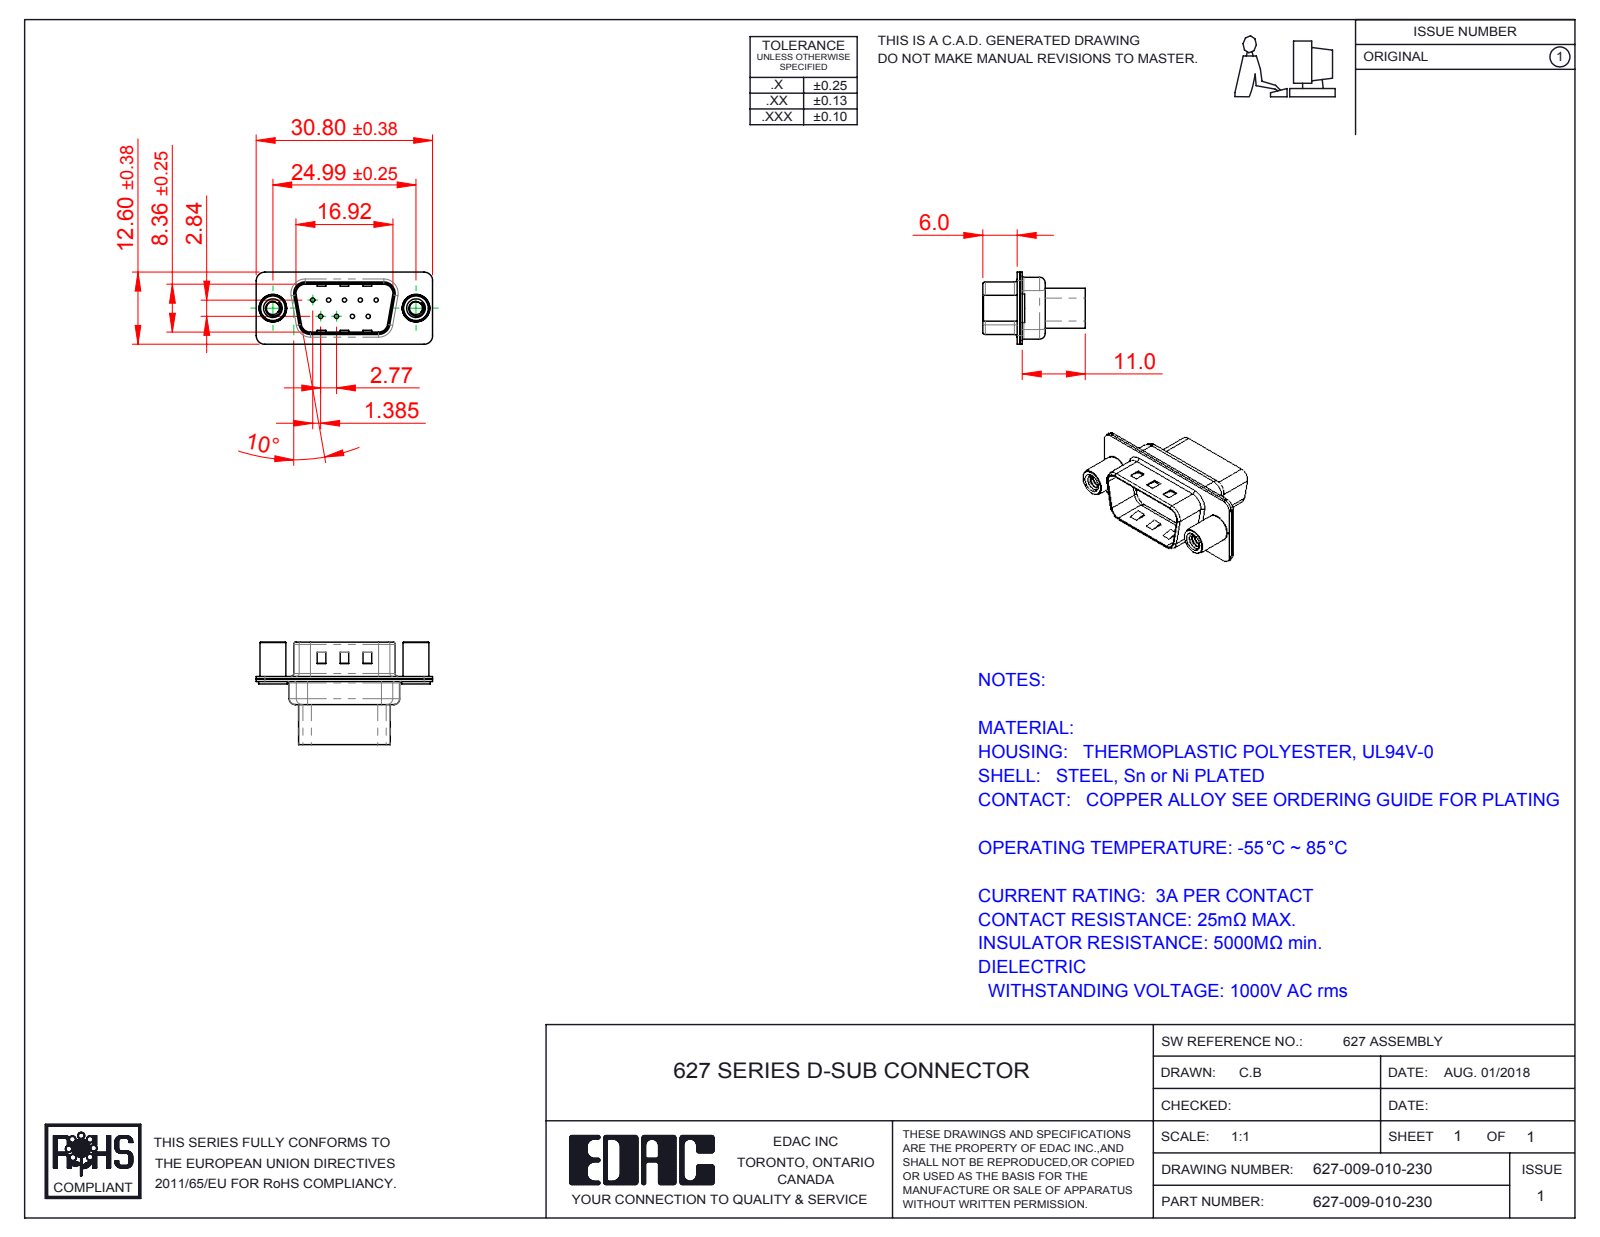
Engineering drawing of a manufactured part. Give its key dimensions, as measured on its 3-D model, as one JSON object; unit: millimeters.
{"part_name": "627 Shell Front_09 Contacts; 627 Housing_09 HP; 627 Shell Rear_09 Contacts; 627-009-010-230 (+1 more)", "step_written_by": "SolidWorks 2016 (CONFIG_CONTROL_DESIGN)", "units": "millimeters", "bodies": {"solids": 5, "faces": 410, "planar": 127, "cylindrical": 211, "other": 72}, "overall_size": [30.8, 17.9, 12.6], "volume_mm3": 1774, "surface_area_mm2": 3800, "round_holes": [[0.75, 9], [1.6, 9], [2, 9], [2.26, 2], [4, 2], [4.8, 2]], "round_bosses_or_shafts": [[5, 2], [4.9, 2], [4.5, 2]], "partial_cylinders_radius": [[1.5, 18], [2, 12], [0.5, 8], [1.6, 8], [0.25, 4], [0.6, 4], [0.65, 4], [0.9, 4]], "face_to_face_distances": [0.4, 0.45, 0.9, 0.82, 9.58, 1.4, 0.68, 7.68, 1.08, 8.08], "hole_center_spacings": [3.16, 2.77, 5.54, 5.03, 5.04, 8.31, 7.48, 7.49]}
